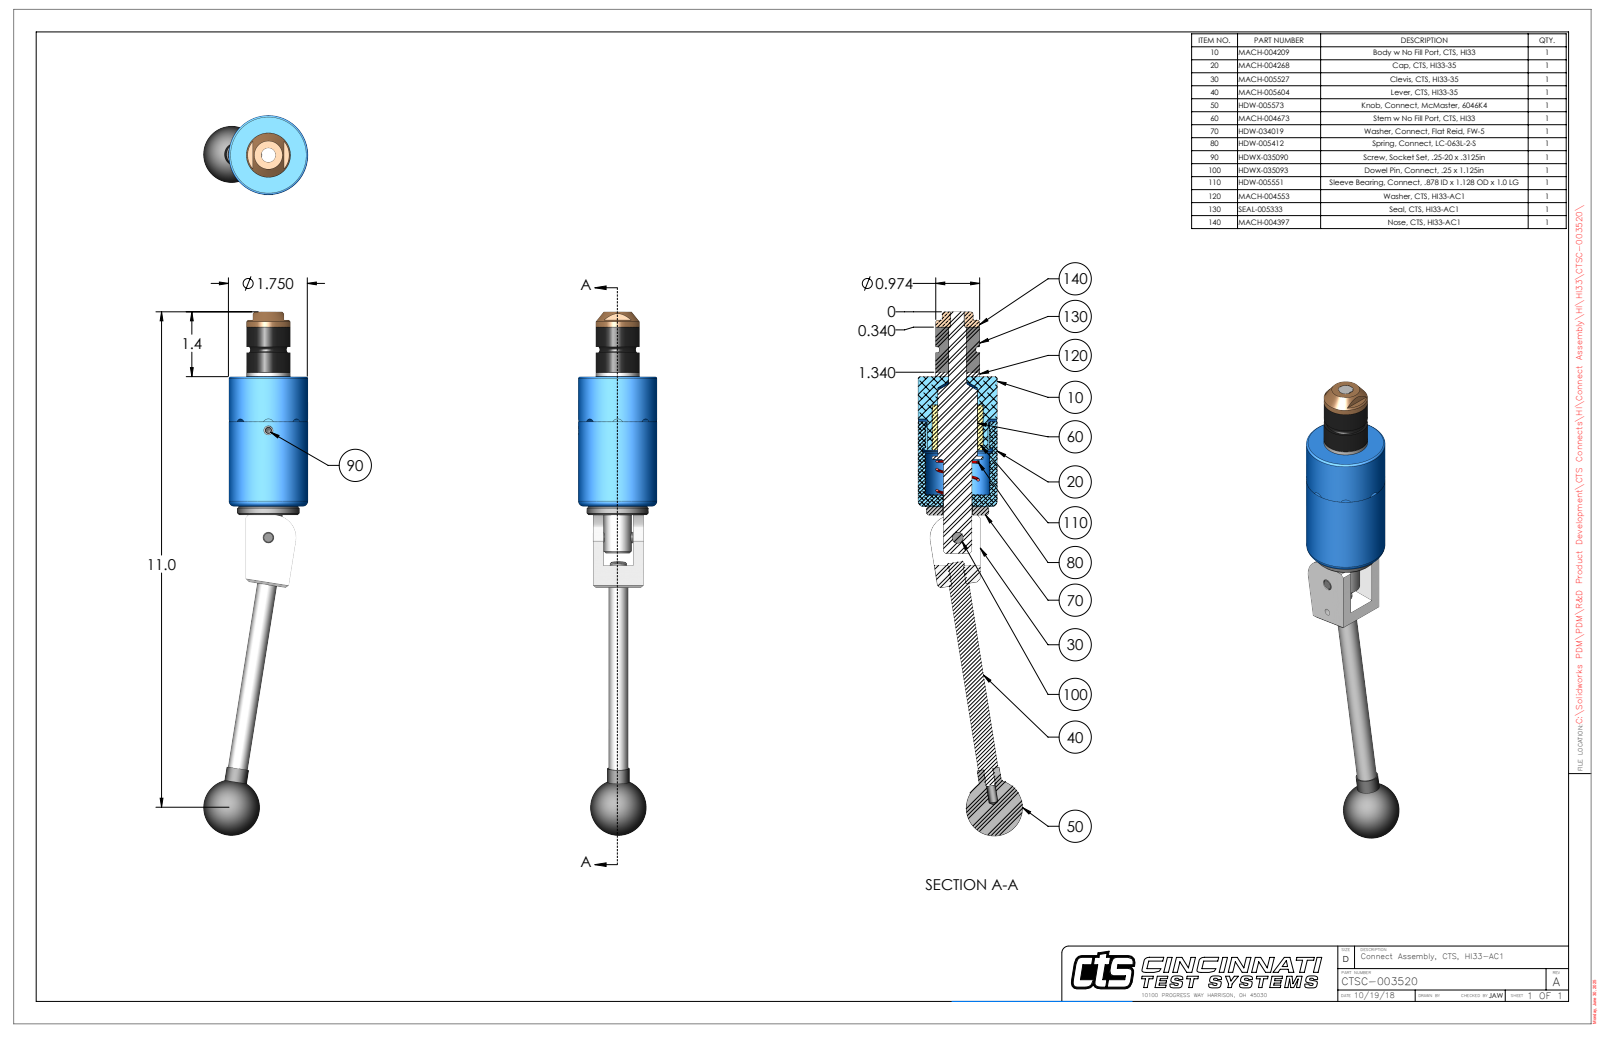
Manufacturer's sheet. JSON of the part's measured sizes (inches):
{"part_name": "CTSC-003520", "step_written_by": "SolidWorks 2023 (AUTOMOTIVE_DESIGN)", "units": "inches", "bodies": {"solids": 9, "faces": 232, "planar": 78, "cylindrical": 95, "other": 59}, "overall_size": [11.613, 2.312, 1.75], "volume_in3": 11.12, "surface_area_in2": 63.07, "round_holes": [[0.201, 2], [0.313, 2], [0.15, 1], [0.249, 1], [0.251, 1], [0.39, 1], [0.397, 1], [0.403, 1], [0.635, 1], [0.656, 1], [1.419, 1]], "round_bosses_or_shafts": [[0.375, 2], [0.312, 2], [0.25, 2], [1.75, 1], [1.38, 1], [0.974, 1], [0.625, 1], [0.5, 1]], "partial_cylinders_radius": [[0.125, 4], [0.029, 2], [0.5, 1], [0.695, 1], [0.837, 1]], "face_to_face_distances": [2.878, 1.098, 1, 1.12, 3.976, 4.164, 3.066, 0.188, 0.098, 2.976], "hole_center_spacings": [0.74, 2.376, 3.116]}
